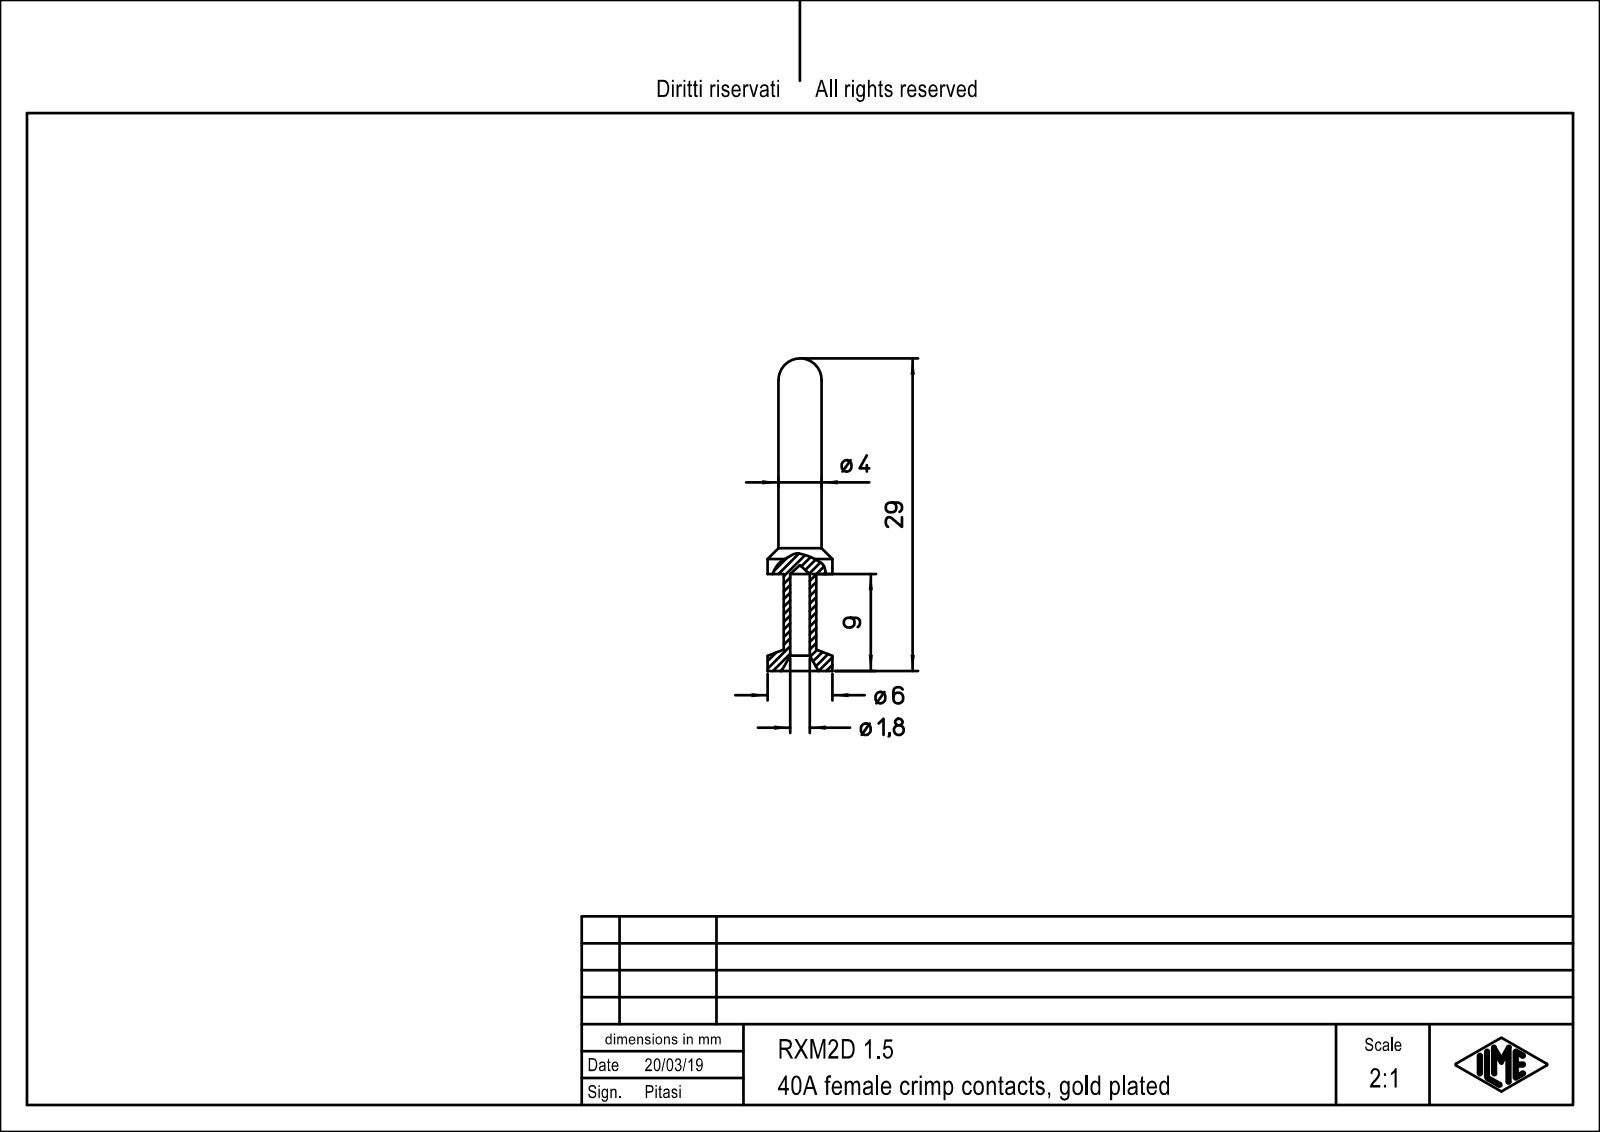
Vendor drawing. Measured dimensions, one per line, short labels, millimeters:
name: RXM2D_1-5
written by: PTC Creo Elements/Direct Modeling 19.0E 27-Jun-2016 (C) Parametric Technology GmbH (AUTOMOTIVE_DESIGN)
unit: mm
bodies: 1 solid, 25 faces (3 planar, 12 cylindrical, 10 other)
size: 29 × 6 × 6
volume: 357 mm³; area: 482 mm²
holes: 1× ⌀1.8
bosses: 1× ⌀6, 1× ⌀4, 1× ⌀3
face distances: 8, 9, 1
